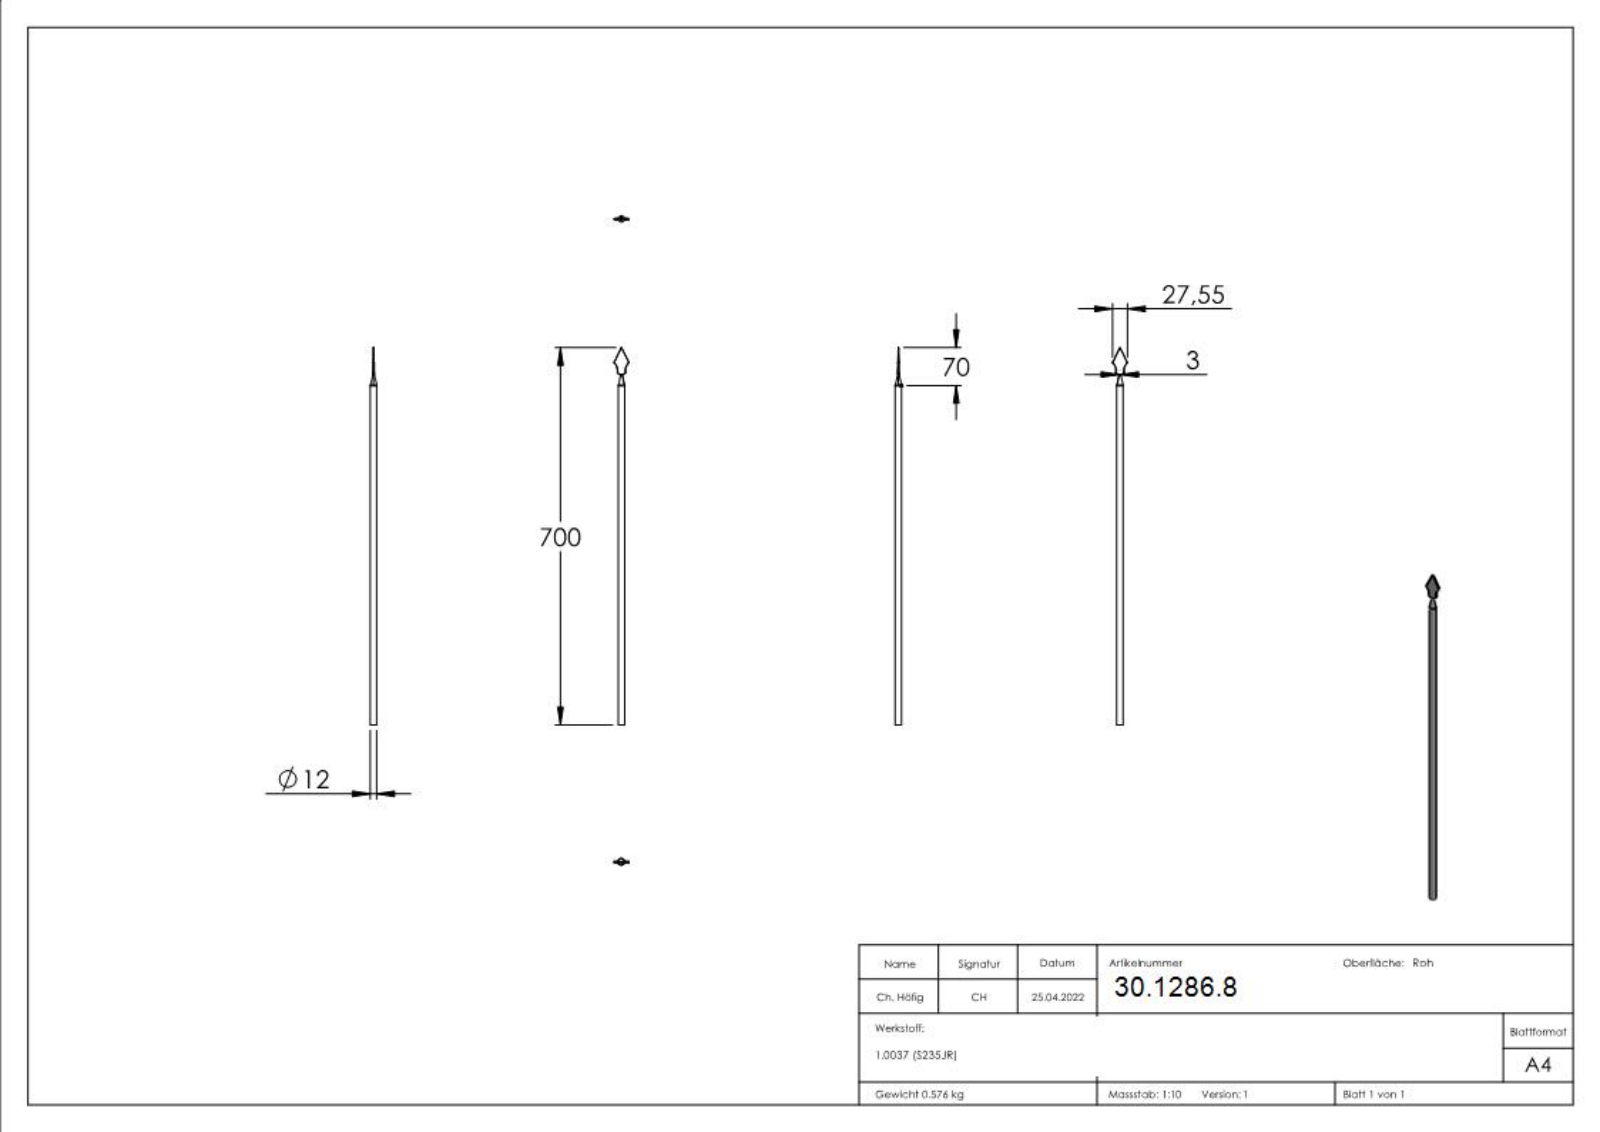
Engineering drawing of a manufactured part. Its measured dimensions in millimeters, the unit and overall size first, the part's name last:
Units: millimetres
Overall size (bounding box): 700 × 27.55 × 12
Round bosses / shafts (diameter × count): ⌀12 ×1, ⌀3 ×1
Partial cylindrical surfaces — rounded edges, fillets, slot ends (radius × count): R1 ×5, R0.5 ×4, R19 ×2, R10 ×1
Main face-to-face distances: 2.21, 0.46, 0.55, 0.68, 0.34, 1.62, 2.2, 0.58, 0.32, 0.93
Volume: 73 826 mm³ · Surface area: 26 101 mm²
Bodies: 1 solid, 252 faces (117 planar, 16 cylindrical, 119 other)
Part name (STEP PRODUCT): 1695
STEP written by: SolidWorks 2018 (CONFIG_CONTROL_DESIGN)
